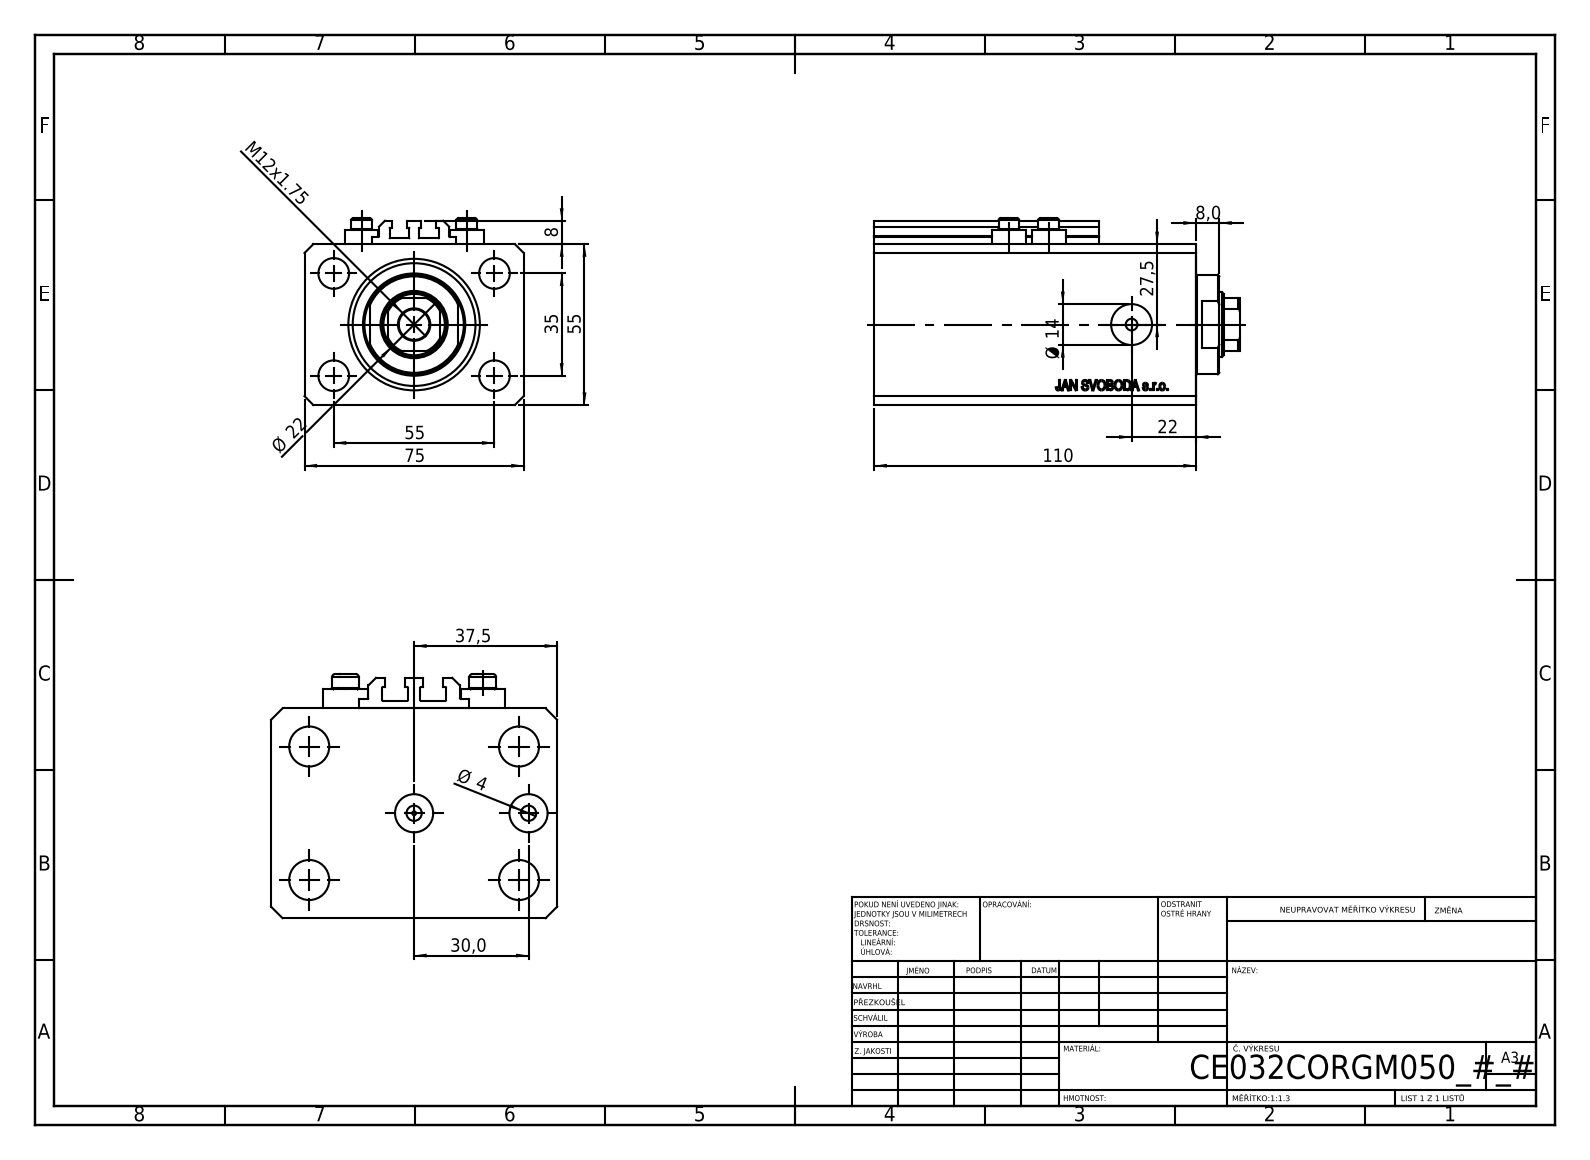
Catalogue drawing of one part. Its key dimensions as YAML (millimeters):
part_name: "V250CE_VC_C; ALLEN BOLT V250CE; V250CE_C_Body; V250CE_C_VCP"
step_written_by: "SolidWorks 2019 (CONFIG_CONTROL_DESIGN)"
units: millimeters
bodies: {solids: 8, faces: 1038, planar: 504, cylindrical: 88, other: 446}
overall_size: [125, 75, 64]
volume: 408447
surface_area: 91607
round_holes:
  - {diameter: 4, count: 8}
  - {diameter: 10.5, count: 5}
  - {diameter: 10, count: 2}
  - {diameter: 14, count: 2}
  - {diameter: 1.25, count: 1}
  - {diameter: 22, count: 1}
  - {diameter: 32, count: 1}
  - {diameter: 45, count: 1}
round_bosses_or_shafts:
  - {diameter: 11.6, count: 4}
  - {diameter: 7, count: 4}
  - {diameter: 34, count: 1}
partial_cylinders:
  - {radius: 0.2, count: 10}
  - {radius: 10.5, count: 1}
face_to_face_distances: [55, 75, 110, 15, 95, 9.9, 85.1, 100.1, 8, 3]
hole_center_spacings: [32.6, 13.6, 17.68, 35, 36, 38.48, 55, 60.1]
